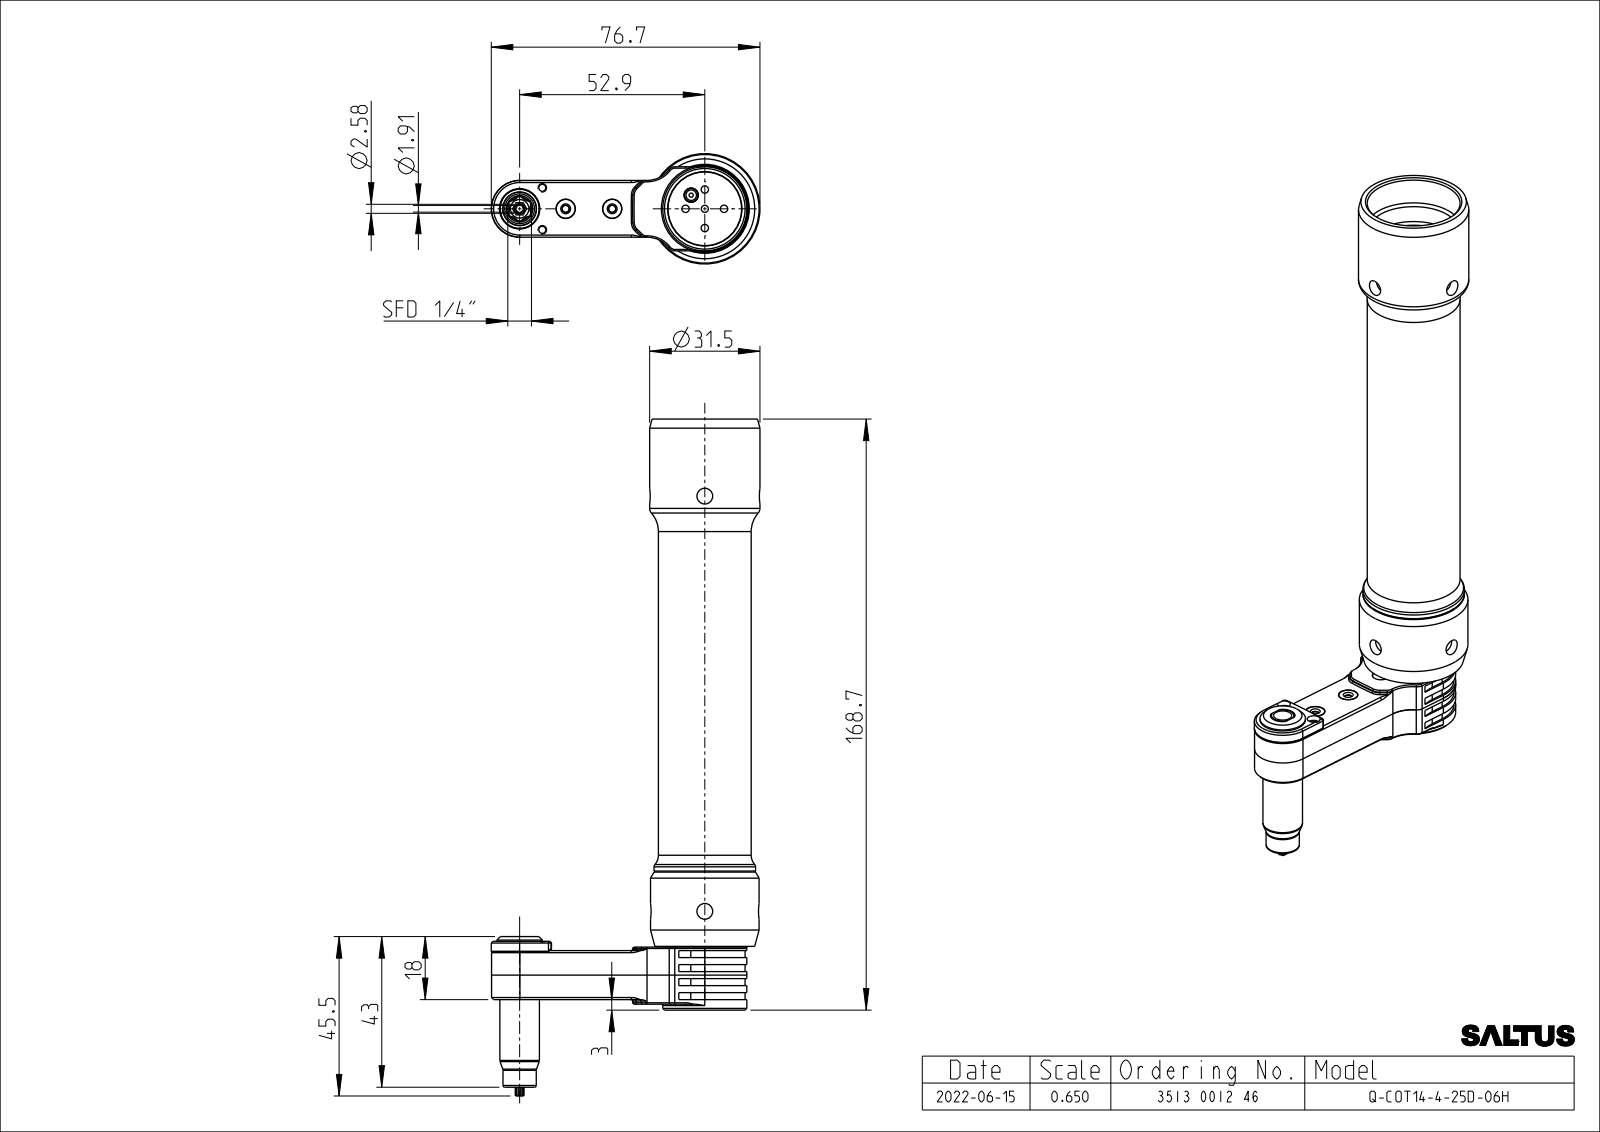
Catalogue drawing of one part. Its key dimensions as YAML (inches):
part_name: "EXT_COMP_SW0003"
step_written_by: "CREO PARAMETRIC BY PTC INC, 2020281 (CONFIG_CONTROL_DESIGN)"
units: inches
bodies: {solids: 2, faces: 549, planar: 135, cylindrical: 237, other: 177}
overall_size: [7.606, 3.021, 1.24]
volume: 7.068
surface_area: 34.24
round_holes:
  - {diameter: 0.079, count: 4}
  - {diameter: 0.083, count: 4}
  - {diameter: 0.177, count: 4}
  - {diameter: 0.081, count: 2}
  - {diameter: 0.102, count: 2}
  - {diameter: 0.142, count: 2}
  - {diameter: 0.144, count: 2}
  - {diameter: 0.217, count: 2}
  - {diameter: 0.161, count: 1}
  - {diameter: 0.197, count: 1}
  - {diameter: 0.205, count: 1}
  - {diameter: 0.453, count: 1}
round_bosses_or_shafts:
  - {diameter: 0.138, count: 2}
  - {diameter: 1.24, count: 1}
  - {diameter: 1.22, count: 1}
  - {diameter: 1.142, count: 1}
  - {diameter: 1.043, count: 1}
  - {diameter: 0.945, count: 1}
  - {diameter: 0.827, count: 1}
  - {diameter: 0.512, count: 1}
partial_cylinders:
  - {radius: 0.039, count: 18}
  - {radius: 0.008, count: 12}
  - {radius: 0.012, count: 12}
  - {radius: 0.011, count: 10}
  - {radius: 0.098, count: 6}
  - {radius: 0.011, count: 5}
  - {radius: 0.016, count: 4}
  - {radius: 0.079, count: 4}
face_to_face_distances: [5.925, 5.933, 0.638, 0.591, 0.118, 0.598, 6.524, 0.709, 0.551, 0.039]
hole_center_spacings: [0.306, 0.472, 0.166, 0.348, 0.348, 0.353, 0.353, 0.4]
